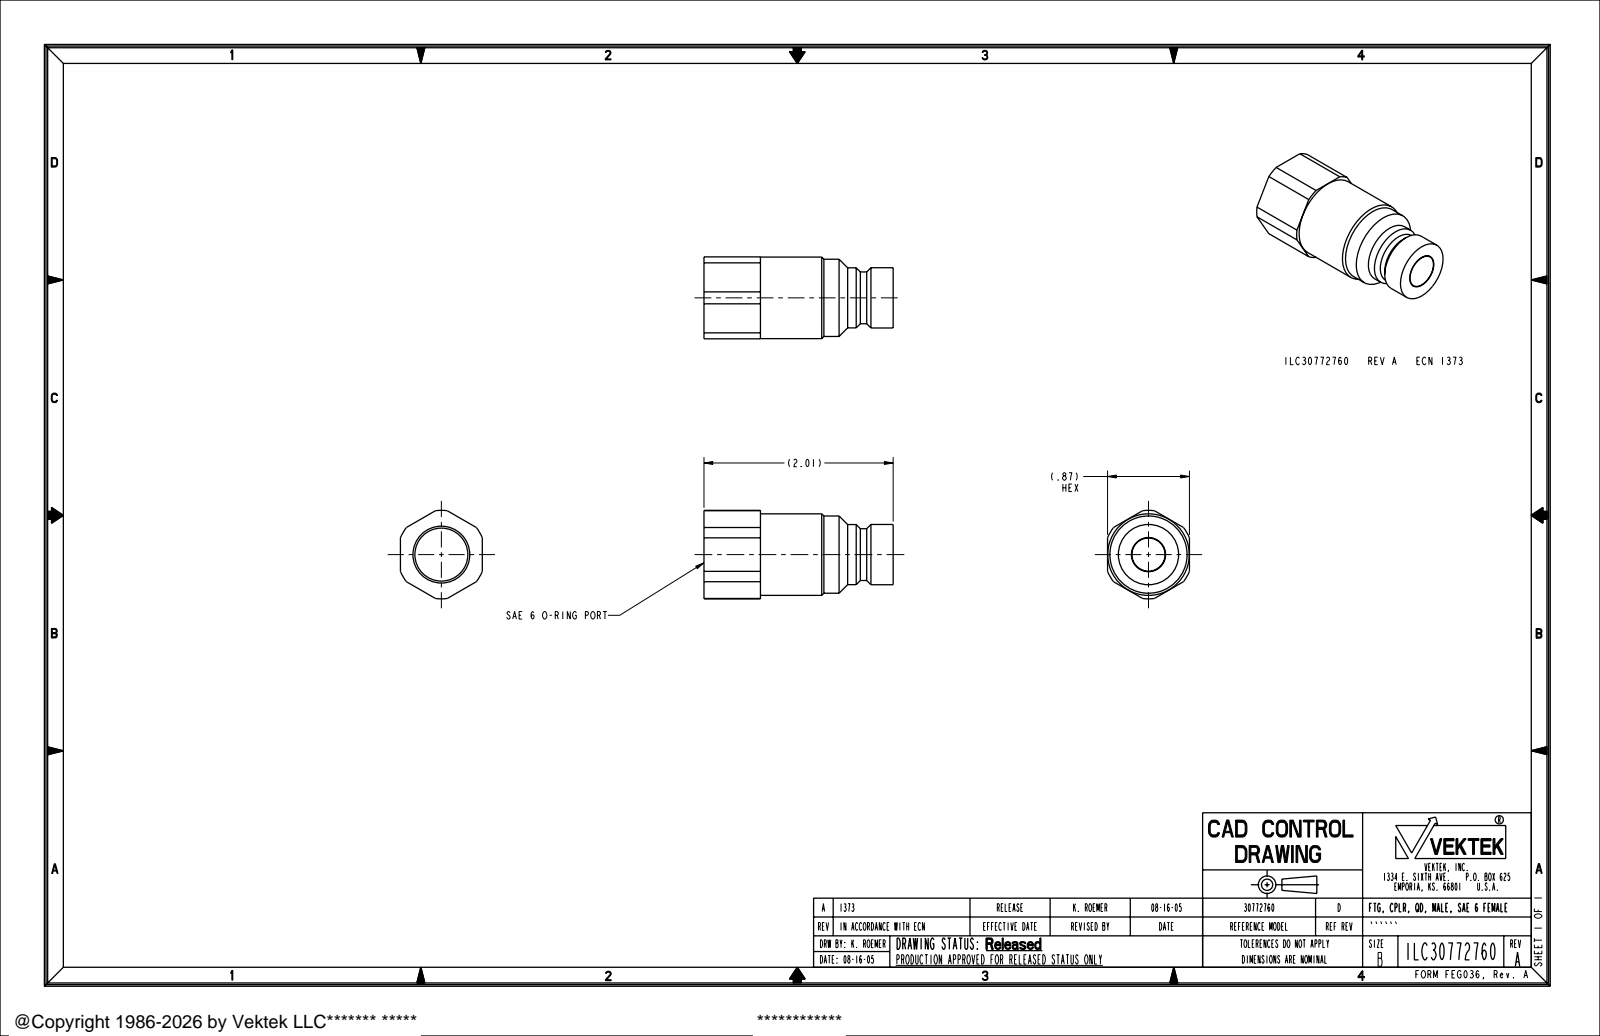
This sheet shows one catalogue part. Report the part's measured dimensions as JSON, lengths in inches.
{"part_name": "ILC30772760", "step_written_by": "PRO/ENGINEER BY PARAMETRIC TECHNOLOGY CORPORATION, 2004290 (AUTOMOTIVE_DESIGN_CC2)", "units": "inches", "bodies": {"solids": 1, "faces": 43, "planar": 11, "cylindrical": 20, "other": 12}, "overall_size": [2.01, 0.94, 0.87], "volume_in3": 0.899, "surface_area_in2": 7.445, "round_holes": [[0.363, 1], [0.563, 1]], "round_bosses_or_shafts": [[0.866, 1], [0.82, 1], [0.64, 1], [0.638, 1], [0.55, 1]], "partial_cylinders_radius": [[0.47, 1]], "face_to_face_distances": [0.87, 2.01, 0.609, 1.401, 0.6, 1.41]}
